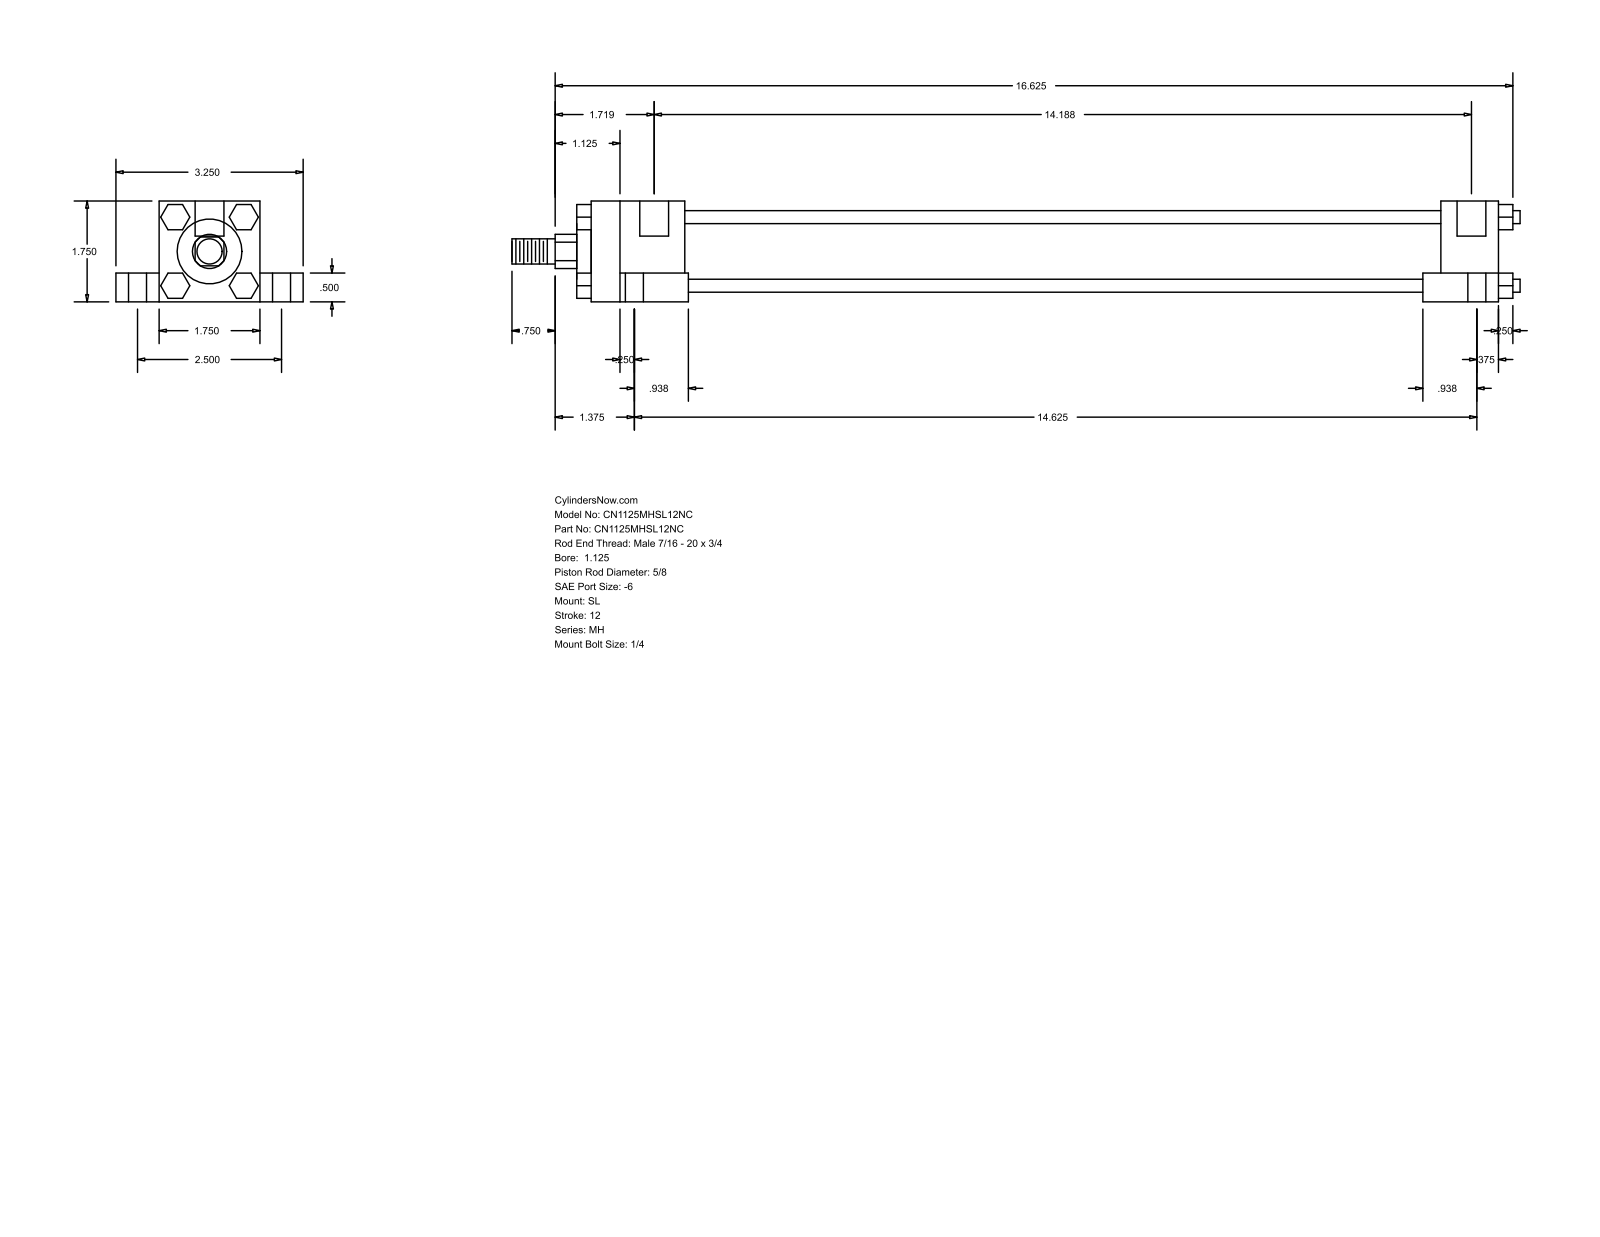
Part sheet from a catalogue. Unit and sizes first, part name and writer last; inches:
Units: inches
Overall size (bounding box): 17.5 × 3.25 × 1.75
Round holes (diameter × count): ⌀0.219 ×4, ⌀0.313 ×4, ⌀0.563 ×4, ⌀0.5 ×2
Round bosses / shafts (diameter × count): ⌀0.225 ×4, ⌀1.375 ×1, ⌀1.125 ×1, ⌀0.625 ×1, ⌀0.437 ×1
Partial cylindrical surfaces — rounded edges, fillets, slot ends (radius × count): R0.297 ×1
Main face-to-face distances: 1.75, 0.75, 0.5, 1.25, 2.5, 0.437, 1.875, 1.313, 13.938, 13.125
Hole centre spacings: 1.254, 1.269, 1.296, 2.5, 14.063, 14.211, 14.336, 14.46
Bodies: 0 solids, 150 faces (114 planar, 36 cylindrical, 0 other)
Part name (STEP PRODUCT): MH_SL__0112_0.625
STEP written by: GSSL Pune (CONFIG_CONTROL_DESIGN)
